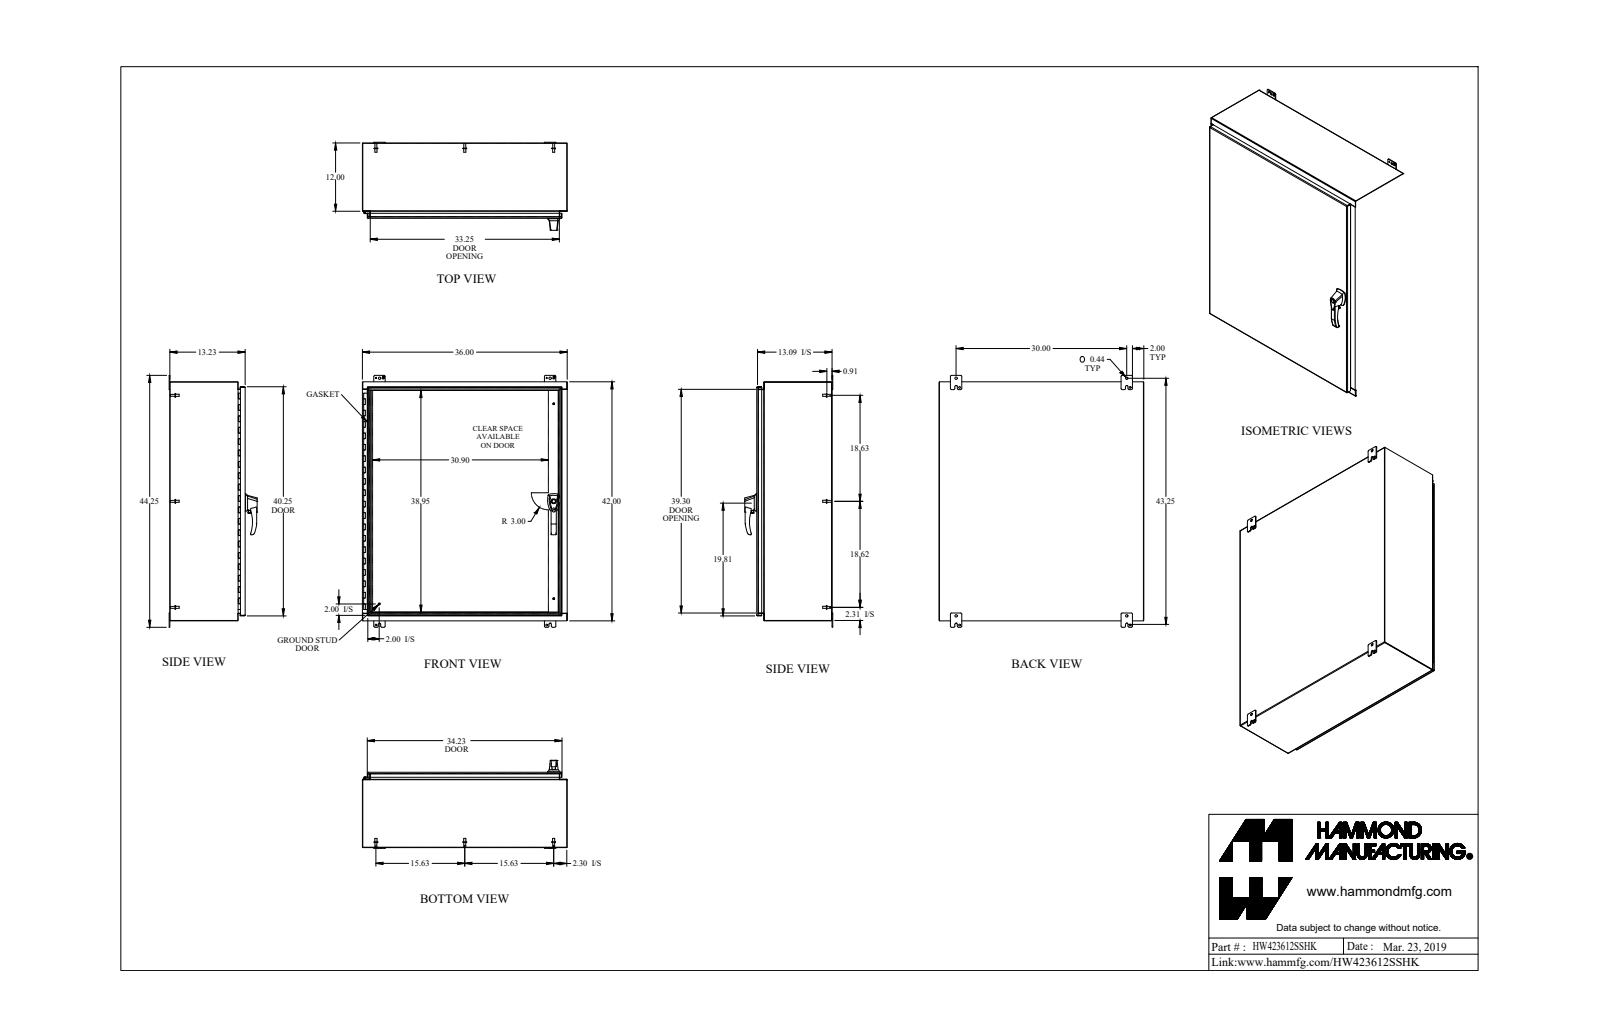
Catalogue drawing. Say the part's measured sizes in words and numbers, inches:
The part is named "HW423612SSHK". Its 3-D file was written by "SolidWorks 2018 (AUTOMOTIVE_DESIGN)". It is 48 solids with 1539 faces: 737 planar, 663 cylindrical and 139 other. Overall it measures 44.25 by 36 by 15.473 inches. Its volume is 457 cubic inches and its surface area 11 316 square inches. Round holes: 6 of diameter 0.176, 5 of diameter 0.313, 3 of diameter 0.25, 3 of diameter 0.265, 3 of diameter 0.413, 2 of diameter 0.196, 2 of diameter 0.256, 2 of diameter 0.394, 2 of diameter 0.437, 1 of diameter 0.187, 1 of diameter 0.233, 1 of diameter 0.33. Round bosses or shafts: 13 of diameter 0.375, 8 of diameter 0.65, 8 of diameter 0.332, 7 of diameter 0.25, 6 of diameter 0.156, 3 of diameter 1, 3 of diameter 0.51, 2 of diameter 0.63. Partial cylindrical surfaces (rounded edges, fillets, slot ends): 27 of radius 0.25, 24 of radius 0.188, 14 of radius 0.036, 14 of radius 0.108, 12 of radius 0.06, 9 of radius 0.125, 8 of radius 0.218, 6 of radius 0.03. The main face-to-face distances are 0.072, 13.138, 13.066, 0.095, 13.233, 13.161, 35.928, 41.928, 35.856, 36. The hole center spacings are 1.111, 17.118, 17.119, 34.237, 17.119, 30, 30.665, 43.38.
